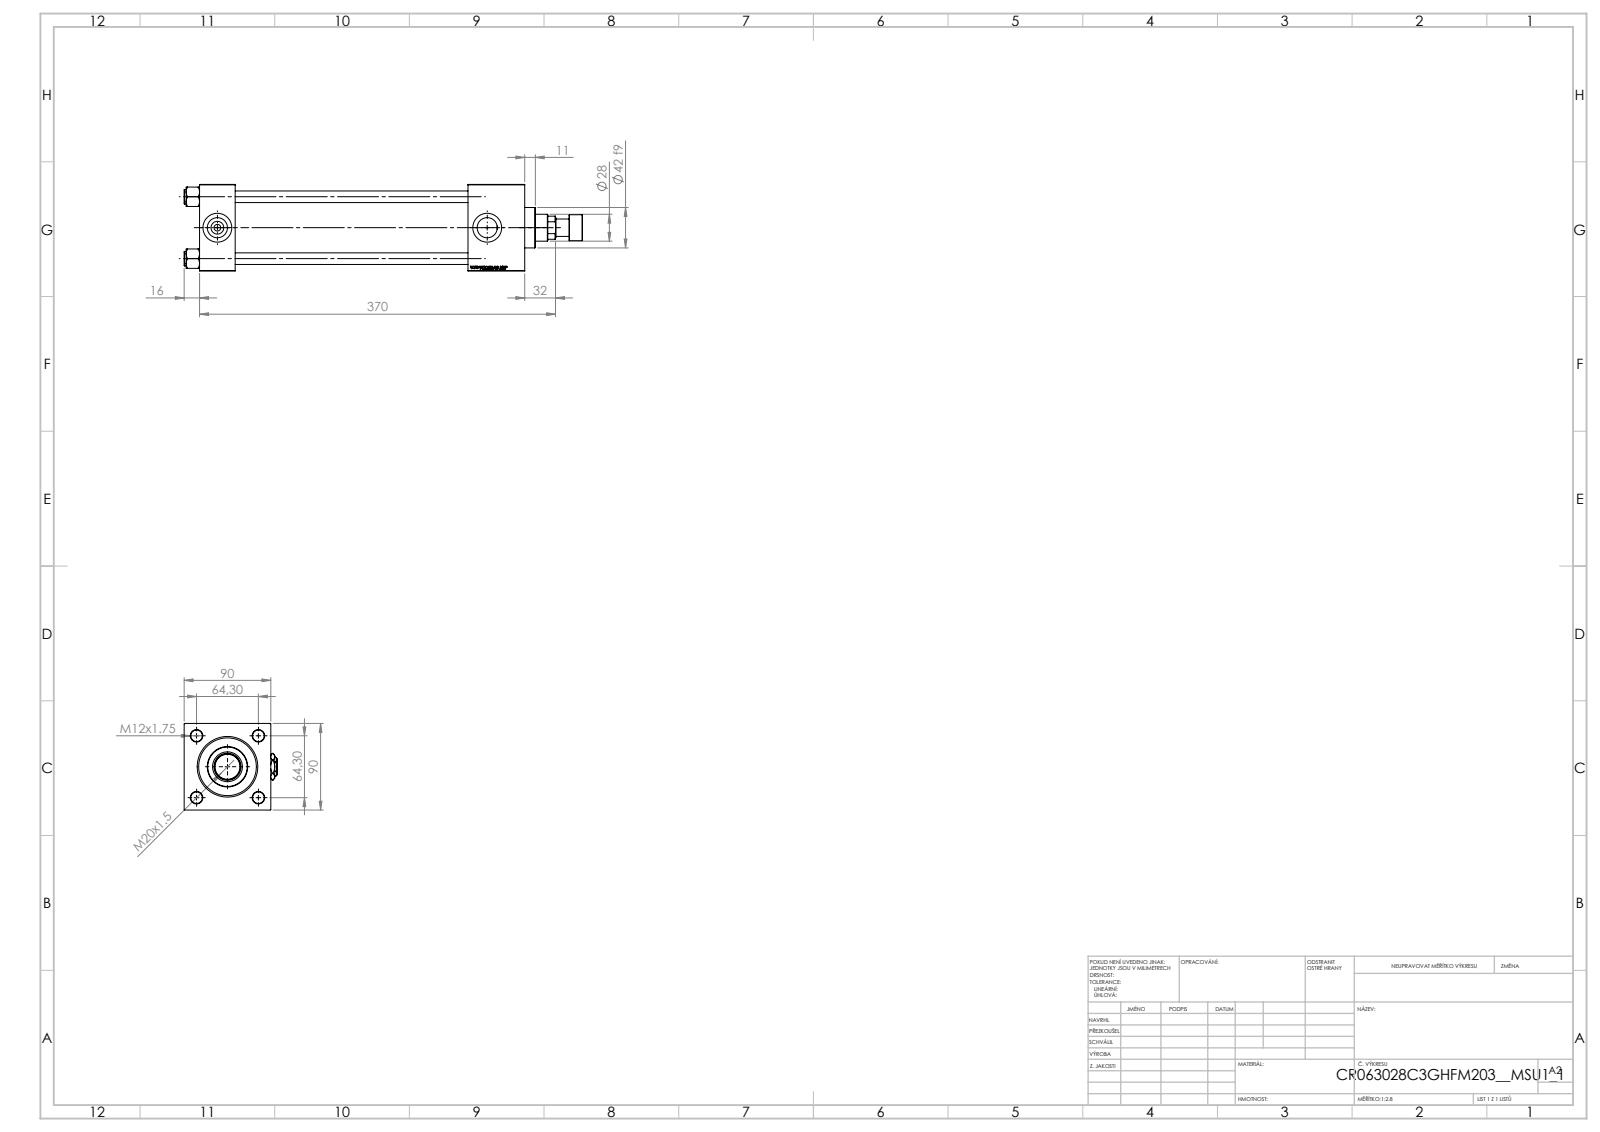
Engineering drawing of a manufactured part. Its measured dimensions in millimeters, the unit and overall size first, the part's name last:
Units: millimetres
Overall size (bounding box): 414 × 97 × 90
Round holes (diameter × count): ⌀12 ×4, ⌀7 ×2, ⌀20.96 ×2, ⌀30 ×2, ⌀18.5 ×1, ⌀28 ×1, ⌀31 ×1, ⌀50 ×1, ⌀60 ×1, ⌀63 ×1
Round bosses / shafts (diameter × count): ⌀15 ×4, ⌀69 ×1, ⌀42 ×1, ⌀27 ×1, ⌀18 ×1
Main face-to-face distances: 90, 37, 301, 338, 59, 279, 242, 309.3, 272.3, 30.3
Hole centre spacings: 45.47, 64.3, 90.93, 280.5
Volume: 1 261 000 mm³ · Surface area: 306 754 mm²
Bodies: 14 solids, 1264 faces (578 planar, 102 cylindrical, 584 other)
Part name (STEP PRODUCT): V215CR_C_Body; V215CR_C_TYCINKA; V215CR_ROD_END_F; V215CR_VCP_C (+3 more)
STEP written by: SolidWorks 2019 (CONFIG_CONTROL_DESIGN)
